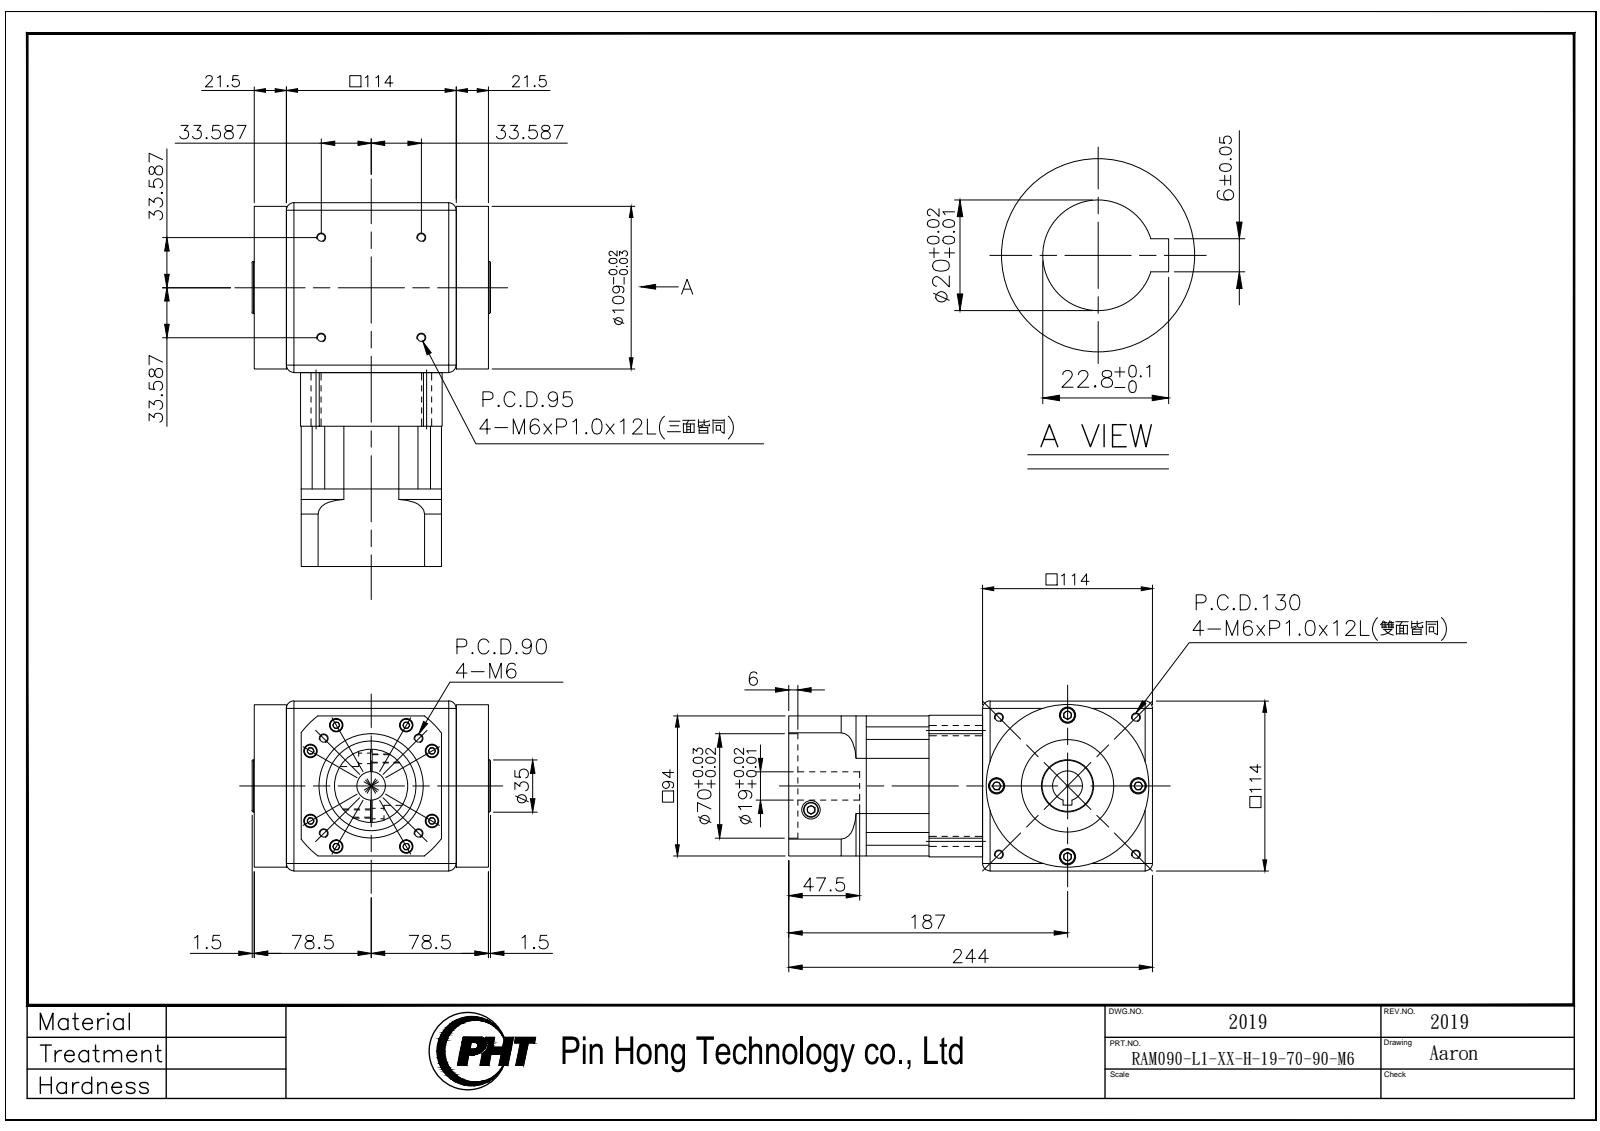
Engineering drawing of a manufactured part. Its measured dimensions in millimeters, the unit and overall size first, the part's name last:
Units: millimetres
Overall size (bounding box): 244 × 160 × 114
Round holes (diameter × count): ⌀5 ×16, ⌀5.2 ×8, ⌀9 ×8, ⌀6.6 ×4, ⌀6.8 ×4, ⌀11 ×4, ⌀12.7 ×2, ⌀19 ×1, ⌀20 ×1, ⌀20.6 ×1, ⌀60 ×1, ⌀70 ×1
Round bosses / shafts (diameter × count): ⌀10 ×8, ⌀8.5 ×8, ⌀109 ×1, ⌀80 ×1, ⌀62 ×1, ⌀49 ×1, ⌀35 ×1
Partial cylindrical surfaces — rounded edges, fillets, slot ends (radius × count): R6 ×4, R50.5 ×1, R59 ×1, R79.1 ×1
Main face-to-face distances: 114, 10, 104, 78, 192, 94, 104.5, 9.5, 0.5, 94.5
Hole centre spacings: 47, 67.18, 12.17, 12.34, 14.08, 45.99, 47.5, 56.03
Volume: 2 786 000 mm³ · Surface area: 230 863 mm²
Bodies: 3 solids, 635 faces (295 planar, 224 cylindrical, 116 other)
Part name (STEP PRODUCT): RAM090-L1-XX-H-19-70-90-M6_2019
STEP written by: SolidWorks 2016 (AUTOMOTIVE_DESIGN)
